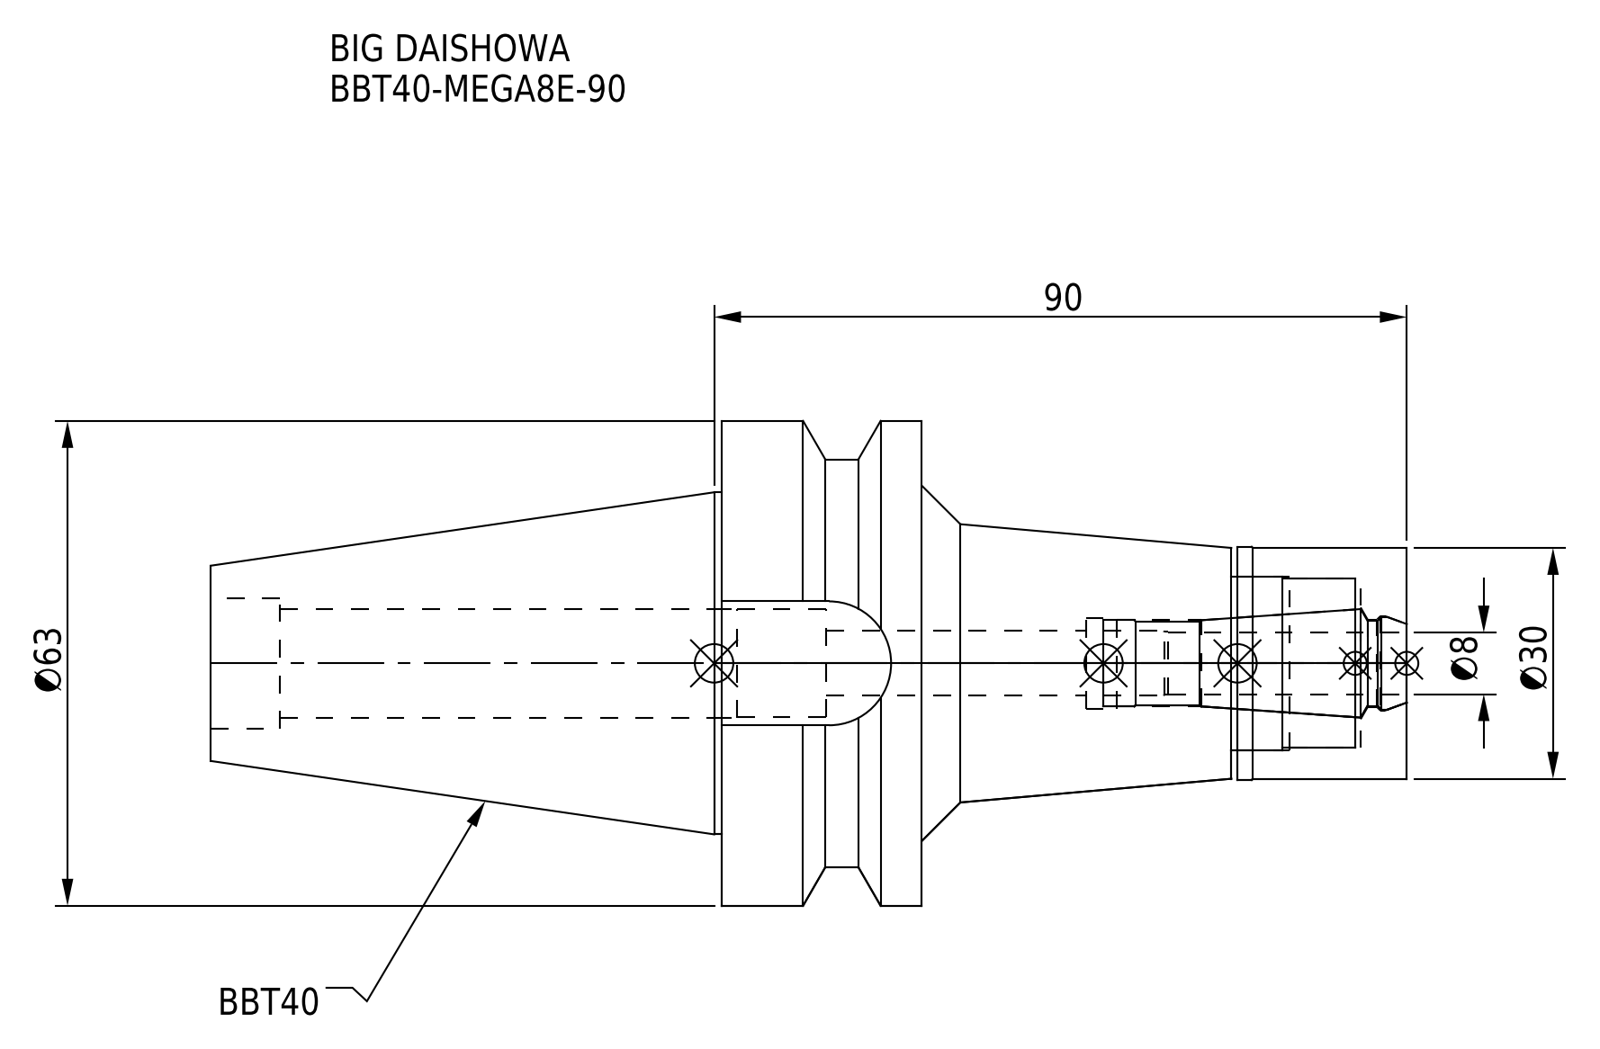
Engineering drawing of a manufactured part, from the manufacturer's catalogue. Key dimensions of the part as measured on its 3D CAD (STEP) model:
Part name (STEP PRODUCT): DXF_TEMP_ASSY_ASM_4_ASM.stp; BBT40-MEGA8E-90; BBT40ME08090-080_ASM.stp; BBT40-MEGA8E-90-080.stp (+3 more)
STEP written by: SolidWorks 2019 (CONFIG_CONTROL_DESIGN)
Units: millimetres
Bodies: 2 solids, 81 faces (21 planar, 40 cylindrical, 20 other)
Overall size (bounding box): 155.4 × 63 × 63
Volume: 168 443 mm³ · Surface area: 33 918 mm²
Round holes (diameter × count): ⌀8.4 ×1, ⌀11.2 ×1, ⌀11.4 ×1, ⌀11.8 ×1, ⌀12.3 ×1, ⌀14 ×1, ⌀14.2 ×1, ⌀17 ×1, ⌀22 ×1, ⌀22.5 ×1
Round bosses / shafts (diameter × count): ⌀63 ×1, ⌀53 ×1, ⌀44.45 ×1, ⌀30.3 ×1, ⌀30 ×1
Partial cylindrical surfaces — rounded edges, fillets, slot ends (radius × count): R8.05 ×1
Main face-to-face distances: 26, 63, 89, 16.1, 45, 22, 41, 67, 22.8, 0.8
